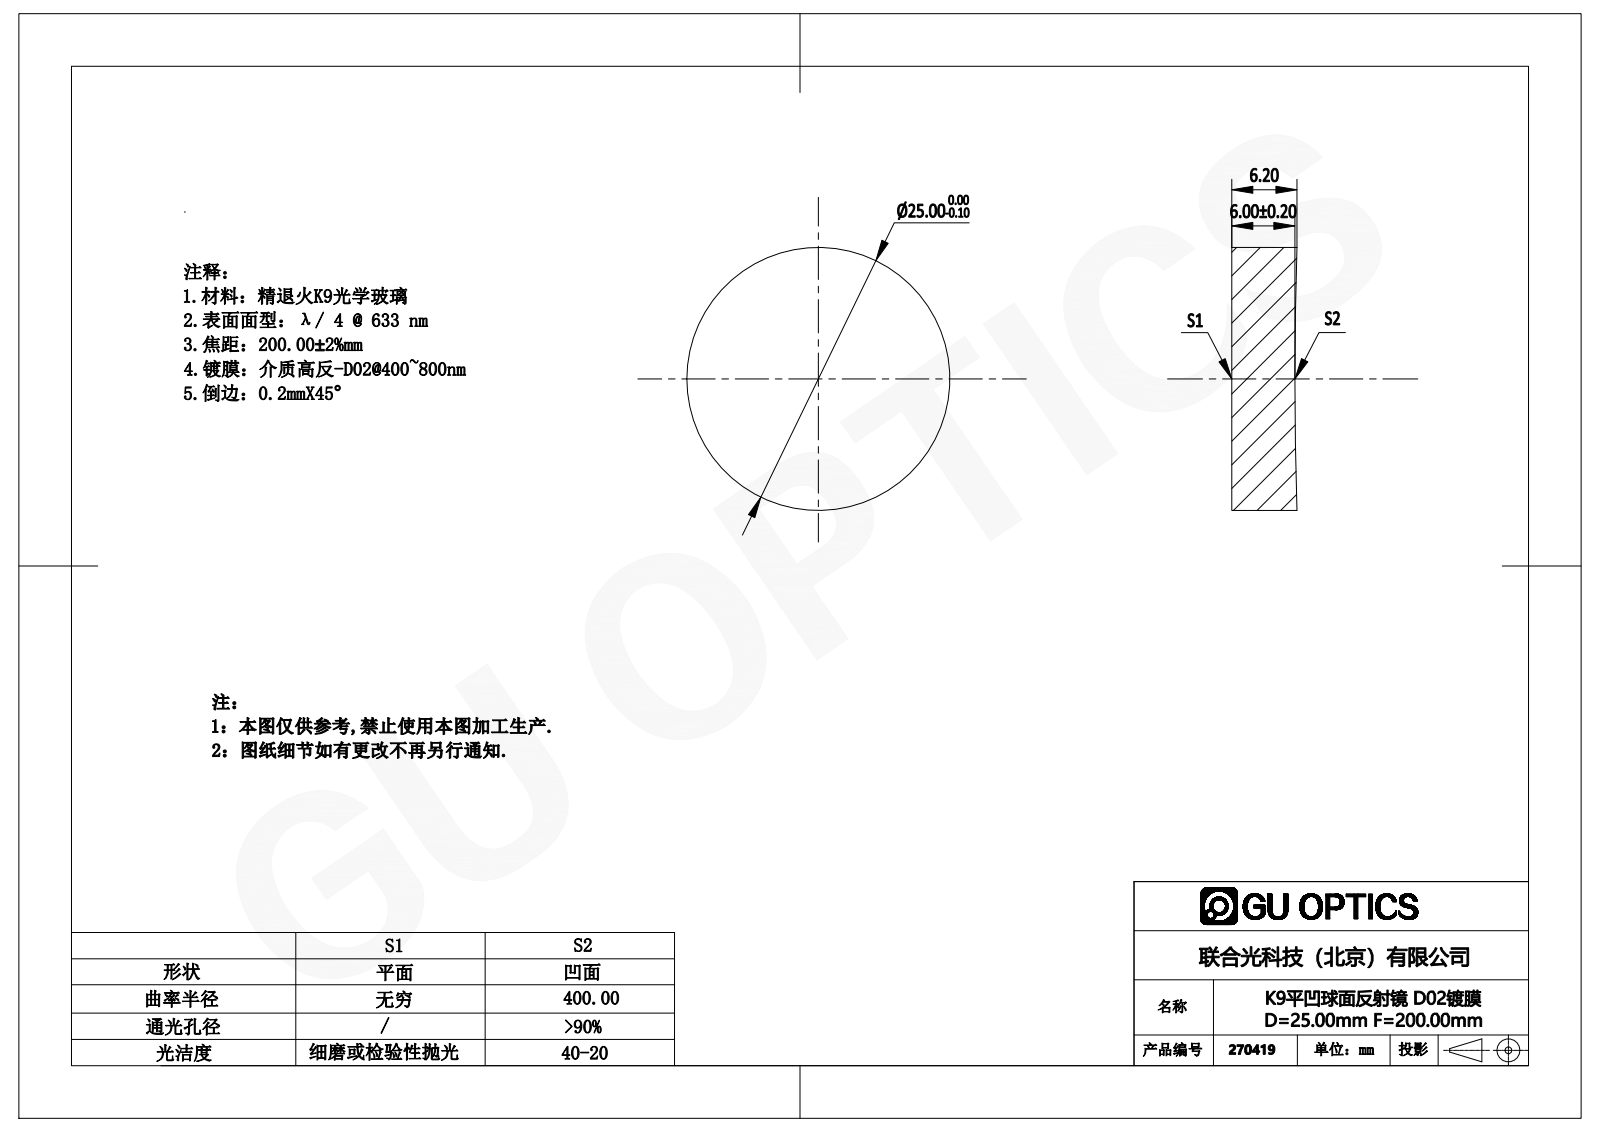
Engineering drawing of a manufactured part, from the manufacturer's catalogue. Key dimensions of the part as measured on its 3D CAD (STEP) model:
Part name (STEP PRODUCT): 270029
STEP written by: SolidWorks 2016 (AUTOMOTIVE_DESIGN)
Units: millimetres
Bodies: 1 solid, 5 faces (1 planar, 2 cylindrical, 2 other)
Overall size (bounding box): 25 × 25 × 6.2
Volume: 2 993 mm³ · Surface area: 1 468 mm²
Round bosses / shafts (diameter × count): ⌀25 ×1
